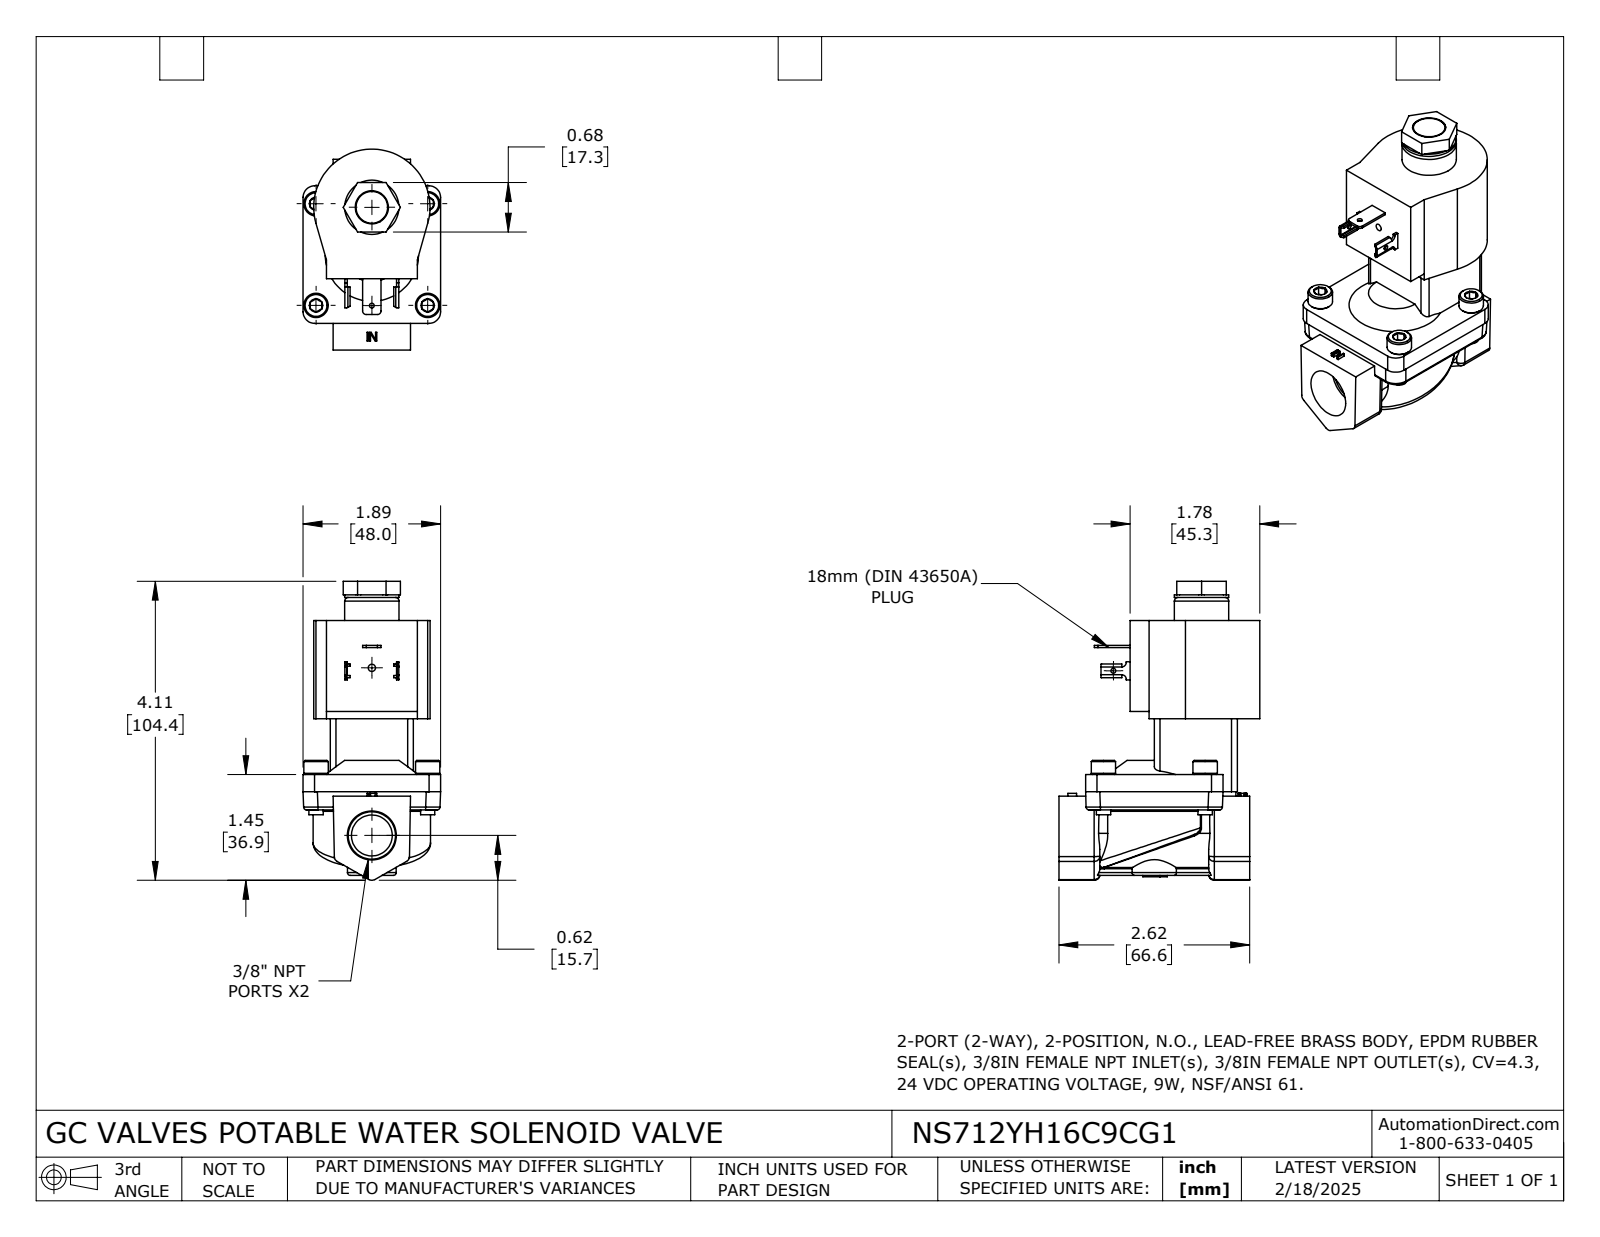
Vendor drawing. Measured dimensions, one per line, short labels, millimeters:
name: NS712YH16C9CG1
written by: SolidWorks 2024 (CONFIG_CONTROL_DESIGN)
unit: mm
bodies: 2 solids, 501 faces (276 planar, 118 cylindrical, 107 other)
size: 104.4 × 70.12 × 48
volume: 137 697 mm³; area: 25 960 mm²
holes: 1× ⌀1.68, 1× ⌀1.7, 1× ⌀2.53, 1× ⌀11.58, 1× ⌀14.27, 1× ⌀30.48
bosses: 4× ⌀8.5, 4× ⌀5, 1× ⌀18.95
rounds: 15× R2, 6× R0.5, 6× R1, 4× R0.15, 4× R1.04, 4× R4, 4× R5, 2× R1.27
face distances: 53.79, 29, 33.3, 37.44, 19.5, 34.29, 9.5, 27, 38.5, 41.74
hole spacings: 34.29, 58.5
